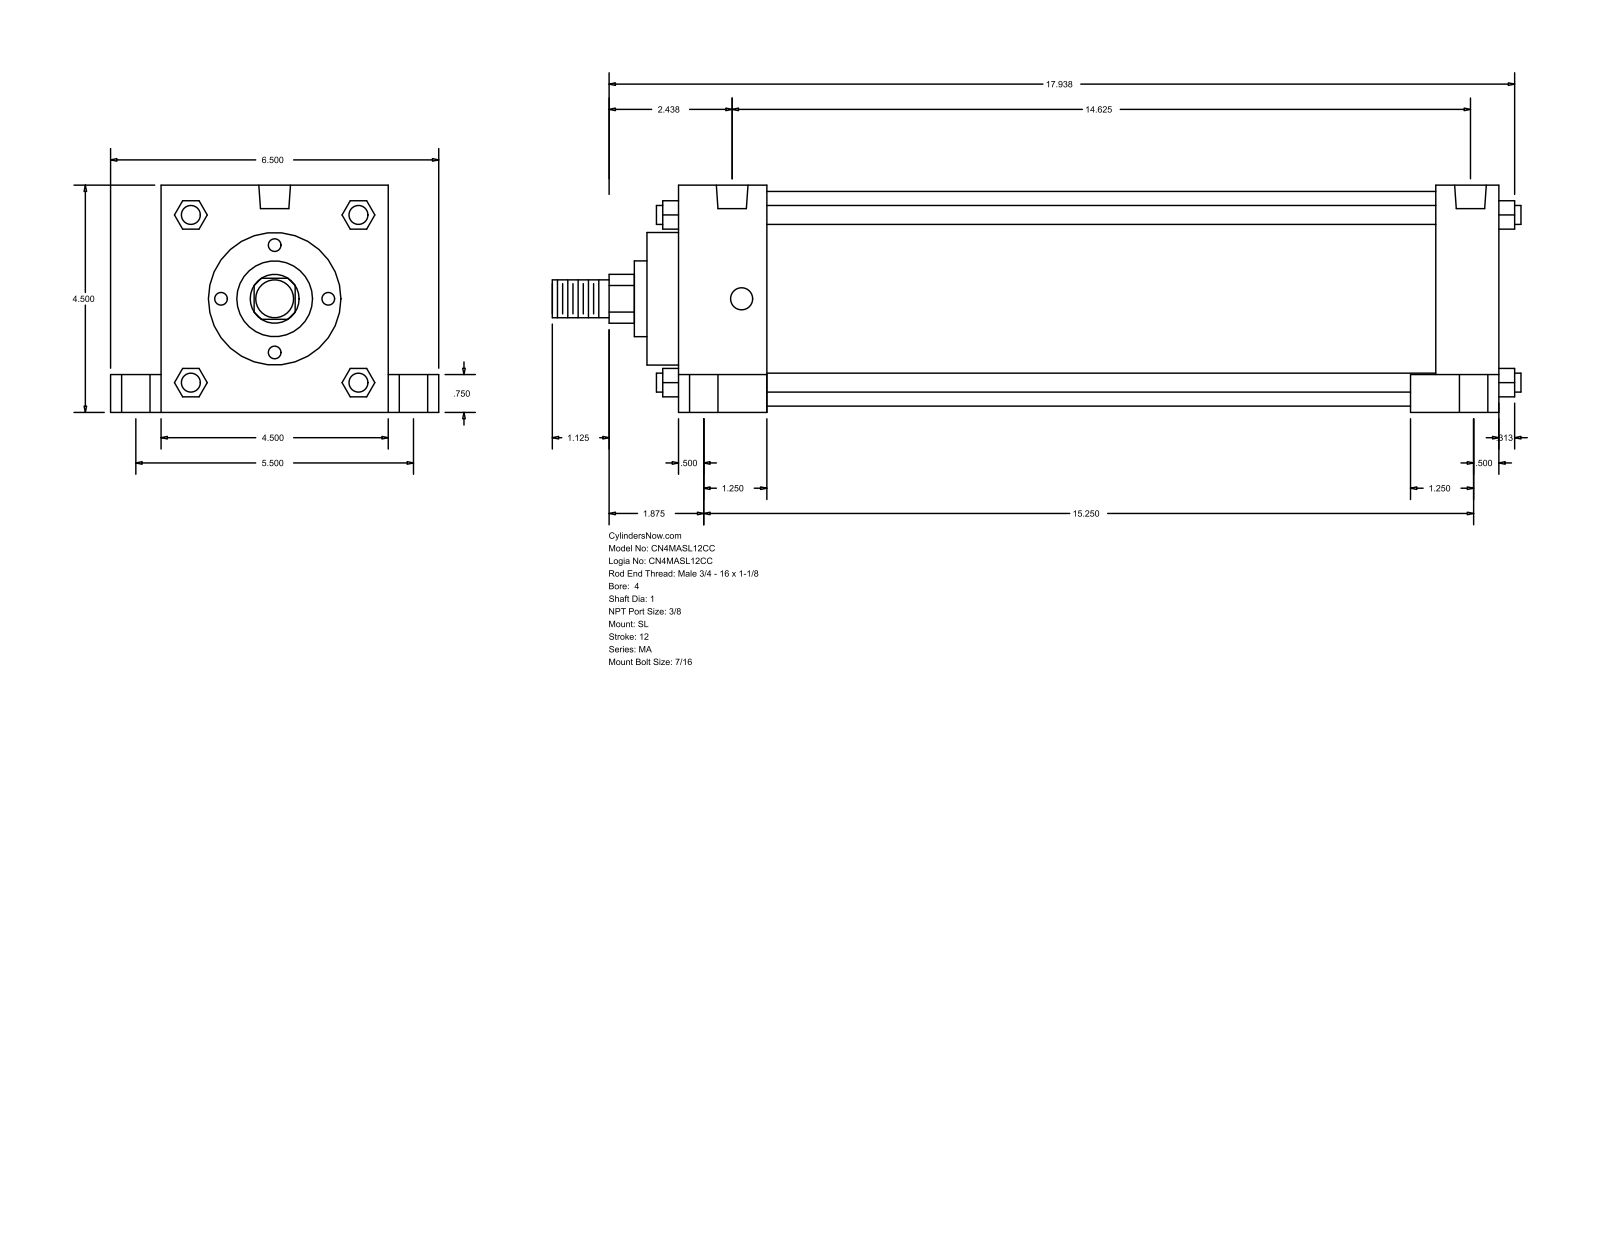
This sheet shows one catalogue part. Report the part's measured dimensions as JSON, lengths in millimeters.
{"part_name": "MA_SL__0400_1", "step_written_by": "GSSL Pune (CONFIG_CONTROL_DESIGN)", "units": "millimeters", "bodies": {"solids": 0, "faces": 150, "planar": 113, "cylindrical": 37, "other": 0}, "overall_size": [487.36, 165.1, 114.3], "round_holes": [[11.11, 4], [14.29, 4], [20.64, 4], [15.93, 2]], "round_bosses_or_shafts": [[9.53, 4], [107.95, 1], [66.67, 1], [38.1, 1], [25.4, 1], [19.05, 1]], "partial_cylinders_radius": [[12.29, 1]], "face_to_face_distances": [114.3, 412.76, 336.55, 44.46, 368.3, 381.01, 31.75, 25.4, 139.7, 19.05], "hole_center_spacings": [69.87, 70.14, 71.3, 72.4, 139.7, 361.95, 374.88, 379.55]}
